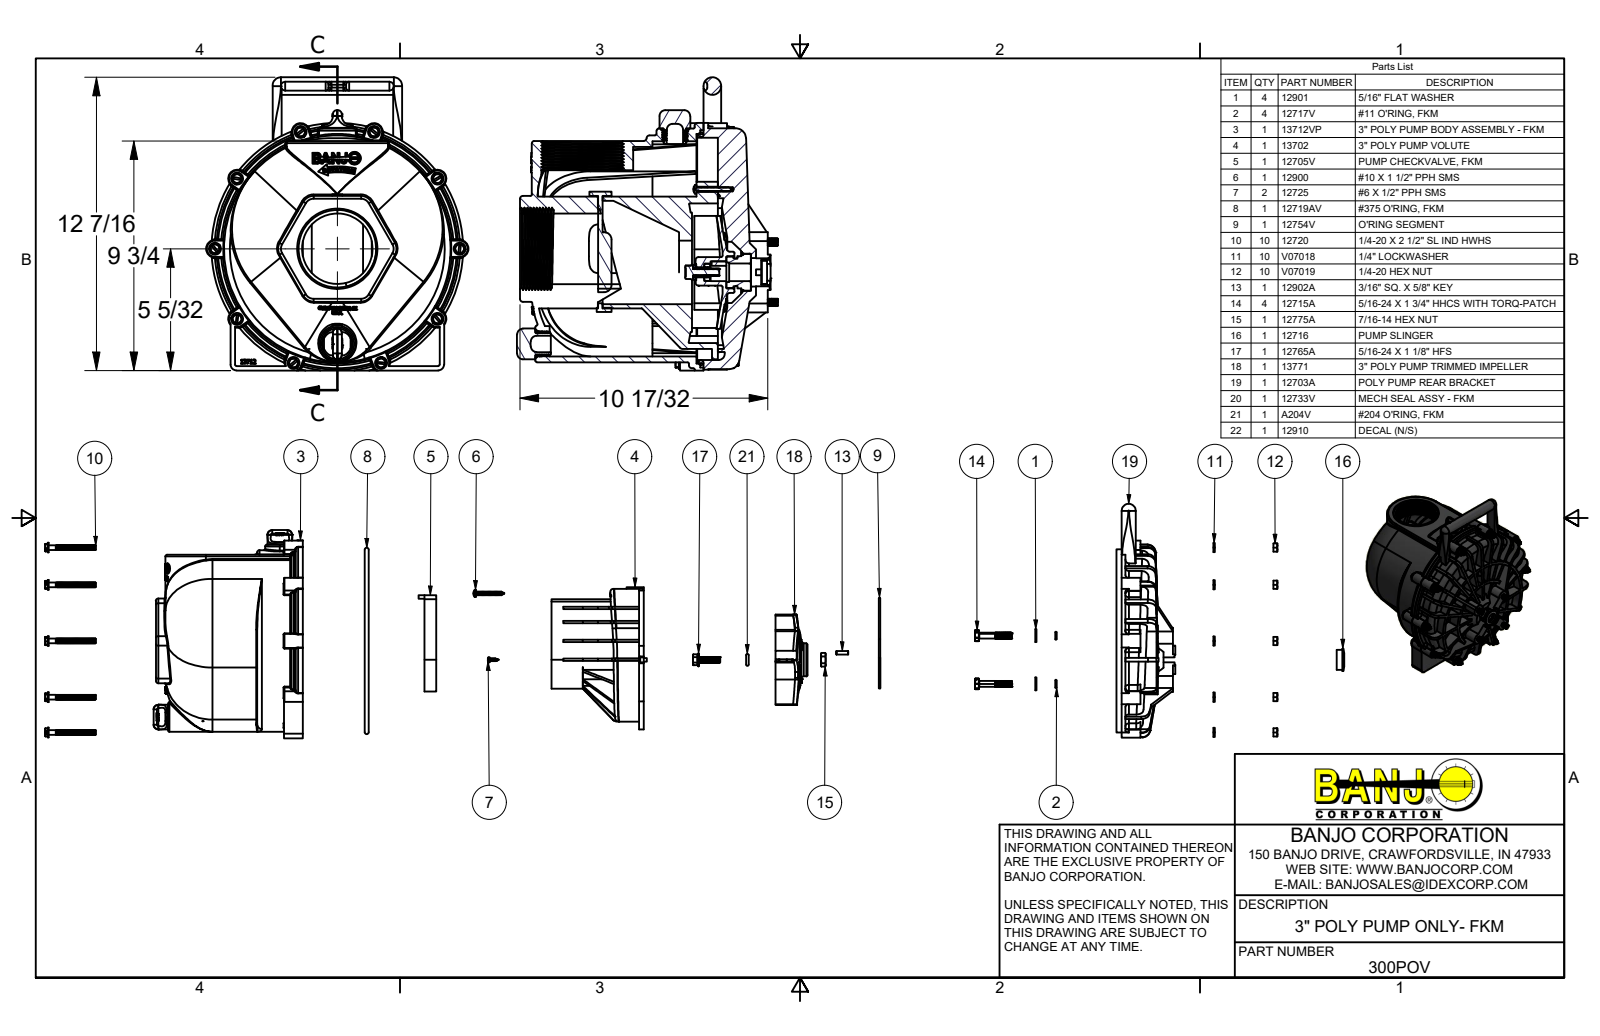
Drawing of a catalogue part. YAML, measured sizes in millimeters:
part_name: "12703A; 13712X; 13777; 13778V (+8 more)"
step_written_by: "Autodesk Inventor 2016 (AUTOMOTIVE_DESIGN)"
units: millimeters
bodies: {solids: 81, faces: 7508, planar: 1818, cylindrical: 2057, other: 3633}
overall_size: [316.27, 283.21, 281.69]
volume: 3250000
surface_area: 1197000
round_holes:
  - {diameter: 4.98, count: 10}
  - {diameter: 6.4, count: 10}
  - {diameter: 6.86, count: 10}
  - {diameter: 5.59, count: 7}
  - {diameter: 8.73, count: 4}
  - {diameter: 11.91, count: 4}
  - {diameter: 20.7, count: 4}
  - {diameter: 2.87, count: 2}
  - {diameter: 2.92, count: 2}
  - {diameter: 5.21, count: 2}
  - {diameter: 6.35, count: 2}
  - {diameter: 7.87, count: 2}
round_bosses_or_shafts:
  - {diameter: 7.02, count: 80}
  - {diameter: 13.21, count: 10}
  - {diameter: 12.42, count: 10}
  - {diameter: 6.35, count: 10}
  - {diameter: 4.88, count: 8}
  - {diameter: 17.48, count: 4}
  - {diameter: 7.94, count: 4}
  - {diameter: 33.27, count: 2}
partial_cylinders:
  - {radius: 0.76, count: 116}
  - {radius: 6.35, count: 27}
  - {radius: 1.52, count: 25}
  - {radius: 4.76, count: 25}
  - {radius: 3.17, count: 24}
  - {radius: 0.38, count: 18}
  - {radius: 9.53, count: 16}
  - {radius: 2.29, count: 8}
face_to_face_distances: [6.35, 25.4, 5.08, 3.17, 15.5, 4.57, 70.62, 4.82, 0.95, 50.8]
hole_center_spacings: [132.08, 65.01, 156.2, 79.43, 132.07, 213.03, 264.16, 45.97]
